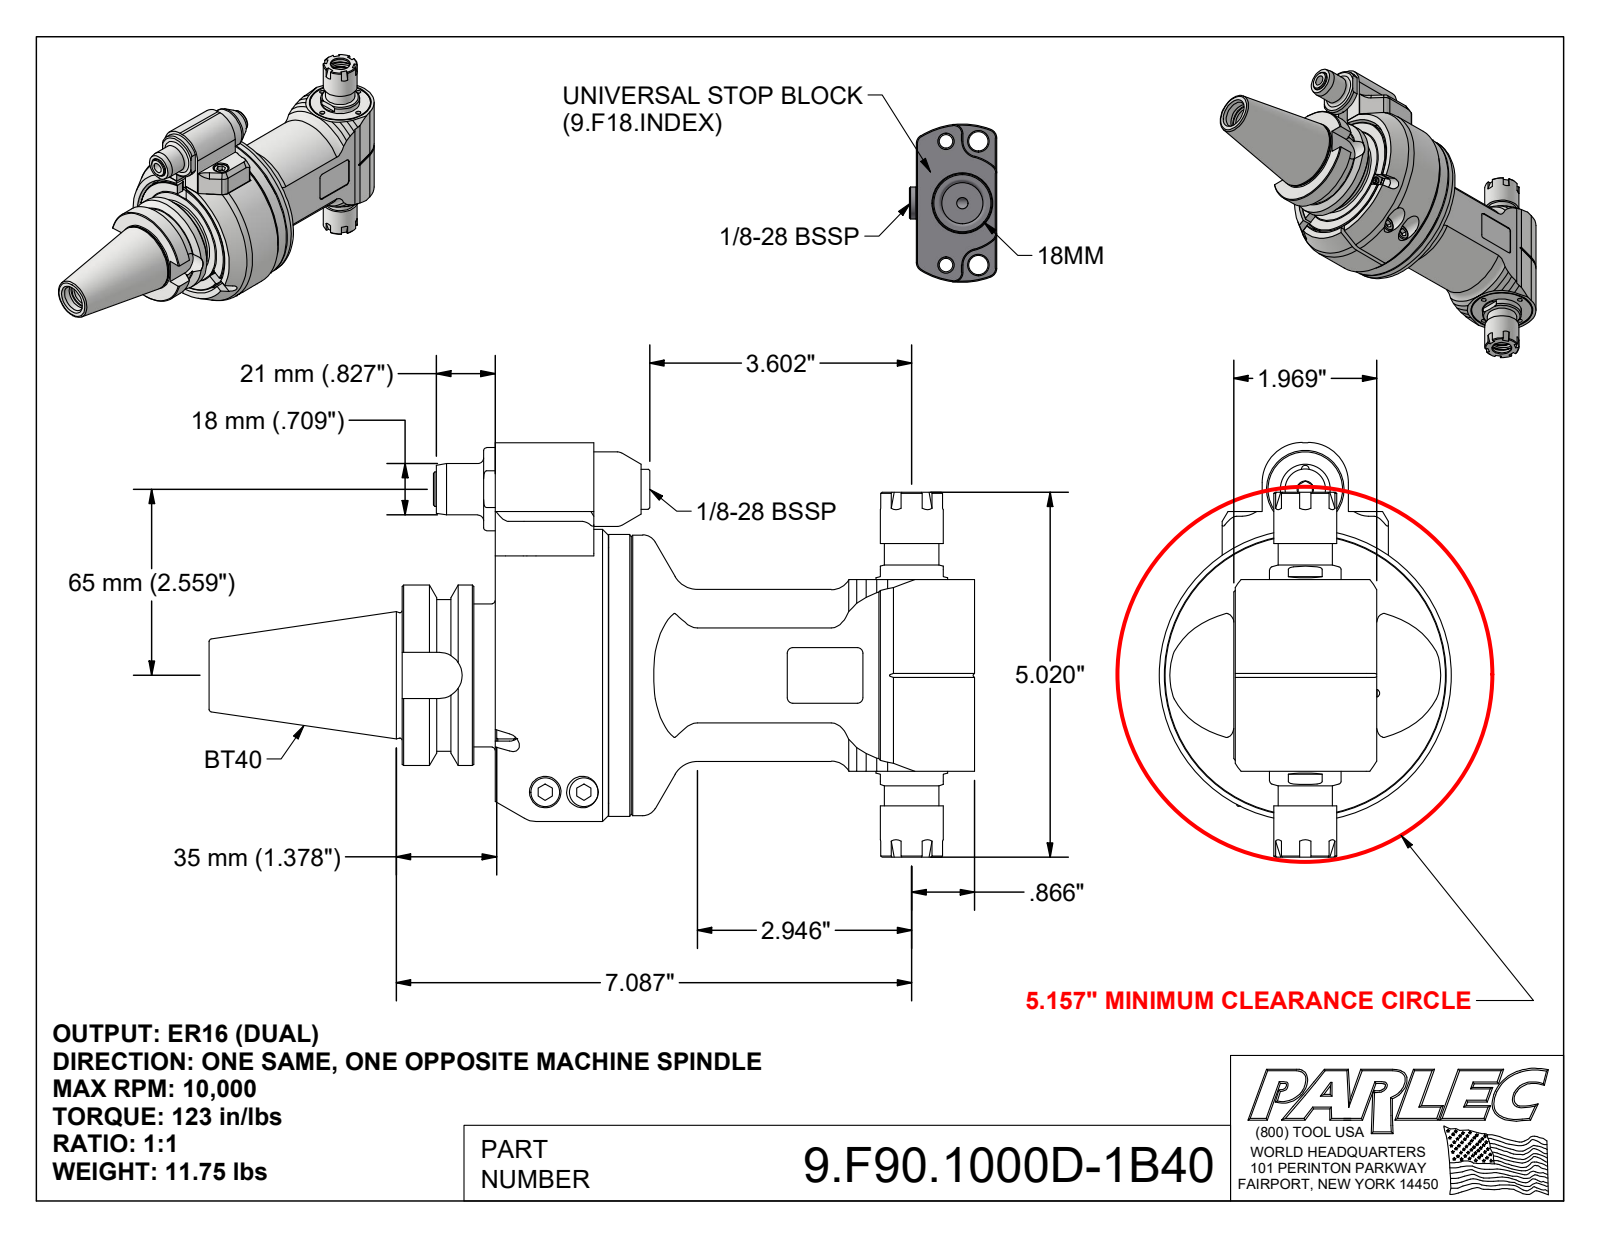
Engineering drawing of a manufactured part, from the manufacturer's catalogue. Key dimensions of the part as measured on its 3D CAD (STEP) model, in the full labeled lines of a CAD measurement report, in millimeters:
Part name (STEP PRODUCT): 9.F90.1000D-1B40; 9_F90_10_2U0; 9_GA1_346_2 (EVO, T
STEP written by: Autodesk Inventor 2025 (AUTOMOTIVE_DESIGN)
Units: millimetres
Bodies: 5 solids, 661 faces (298 planar, 160 cylindrical, 203 other)
Overall size (bounding box): 267.4 × 144.8 × 102
Volume: 917 300 mm³ · Surface area: 154 100 mm²
Round holes (diameter × count): ⌀8.5 ×20, ⌀1.6 ×4, ⌀3.2 ×4, ⌀11 ×3, ⌀2.6 ×2, ⌀4.2 ×2, ⌀5 ×2, ⌀10.4 ×2, ⌀2.5 ×1, ⌀3 ×1, ⌀6.5 ×1, ⌀7 ×1
Round bosses / shafts (diameter × count): ⌀10 ×4, ⌀6 ×4, ⌀18 ×2, ⌀8 ×2, ⌀2.5 ×2, ⌀102 ×1, ⌀98.4 ×1, ⌀98 ×1
Partial cylindrical surfaces — rounded edges, fillets, slot ends (radius × count): R2 ×12, R4 ×4, R0.4 ×2, R0.5 ×2, R1 ×2, R3.5 ×2, R5 ×2, R14 ×2
Main face-to-face distances: 39.5, 32, 7.5, 0.5, 8.5, 7, 8, 32.5, 1, 67
Hole centre spacings: 38.5, 46.3, 37.3, 54.5, 76.3, 10.7, 58.2, 61.5
